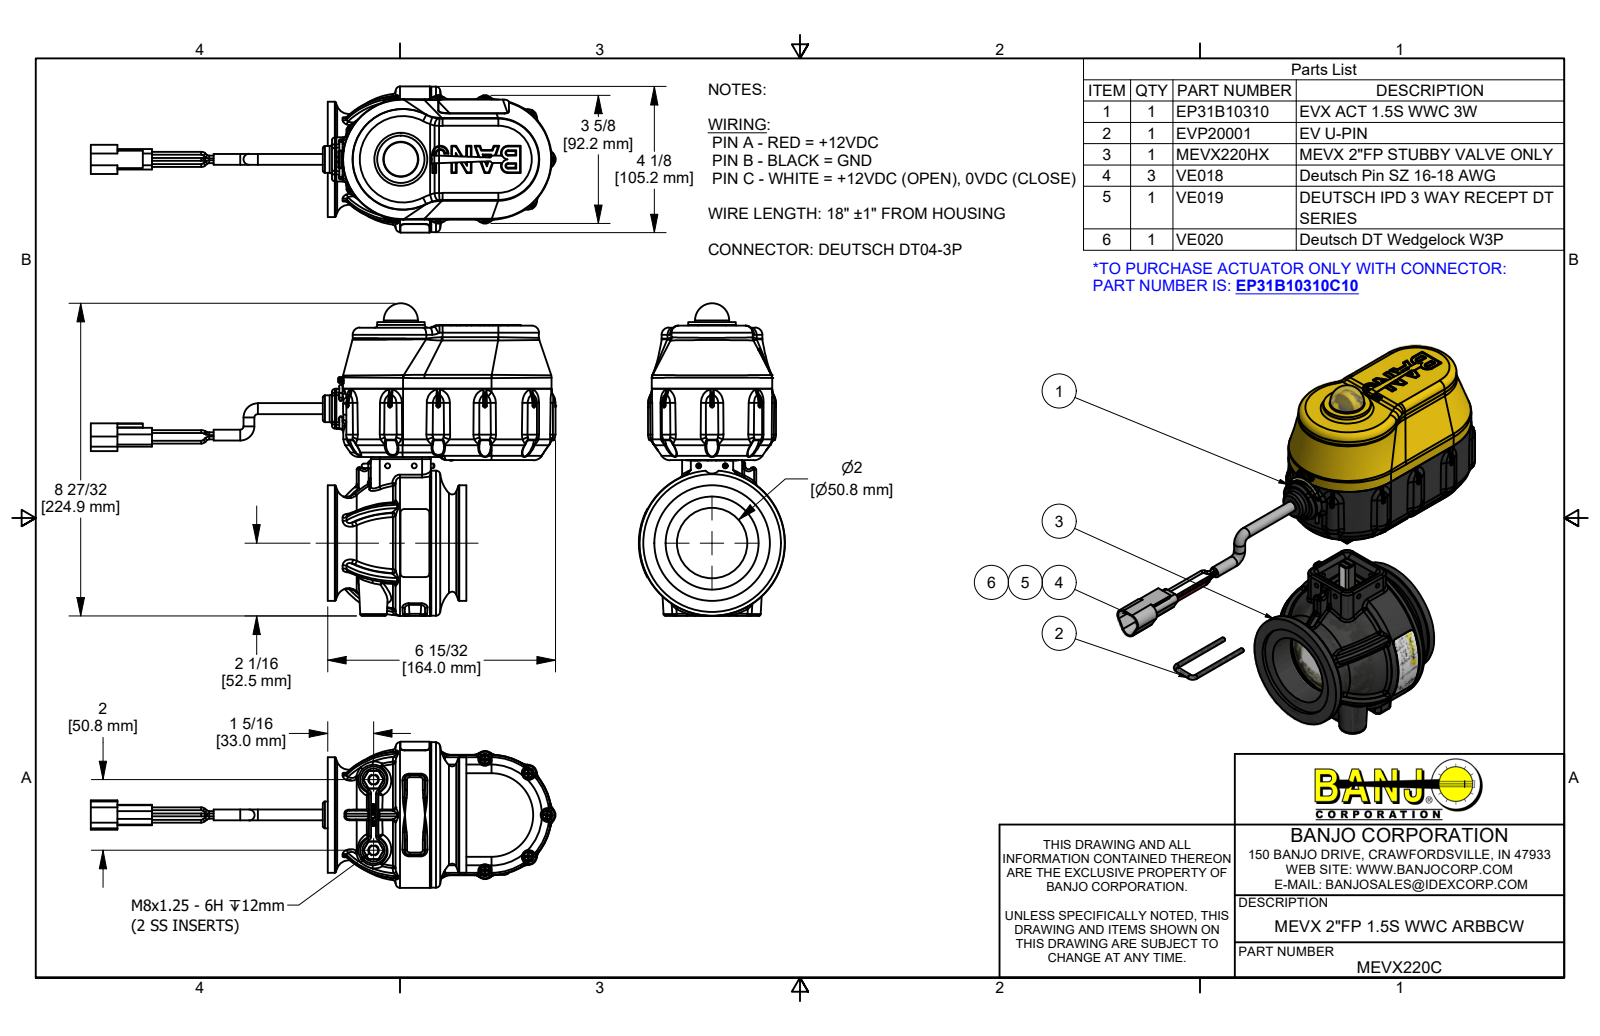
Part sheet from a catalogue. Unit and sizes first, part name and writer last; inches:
Units: inches
Overall size (bounding box): 13.165 × 8.856 × 4.14
Round holes (diameter × count): ⌀0.095 ×11, ⌀0.15 ×11, ⌀0.08 ×7, ⌀0.135 ×5, ⌀0.107 ×4, ⌀0.126 ×4, ⌀0.136 ×4, ⌀0.148 ×4, ⌀0.15 ×4, ⌀0.17 ×4, ⌀0.02 ×3, ⌀0.06 ×3
Round bosses / shafts (diameter × count): ⌀0.25 ×17, ⌀0.08 ×15, ⌀0.14 ×11, ⌀0.108 ×11, ⌀0.085 ×11, ⌀0.058 ×6, ⌀0.27 ×4, ⌀0.219 ×4
Partial cylindrical surfaces — rounded edges, fillets, slot ends (radius × count): R0.013 ×180, R0.04 ×145, R0.01 ×84, R0.02 ×76, R0.005 ×55, R0.03 ×34, R0.06 ×31, R0.08 ×28
Main face-to-face distances: 0.1, 2.565, 0.06, 0.211, 0.151, 1.896, 1.836, 1.685, 0.569, 0.629
Hole centre spacings: 2.22, 0.975, 1.283, 2.69, 2.715, 0.33, 1.095, 1.662
Volume: 53.49 in³ · Surface area: 615.2 in²
Bodies: 89 solids, 10920 faces (2894 planar, 3125 cylindrical, 4901 other)
Part name (STEP PRODUCT): MEVX220C; EP31B10310; B61905PPHS; B632038PM (+8 more)
STEP written by: Autodesk Inventor 2019 (AUTOMOTIVE_DESIGN)
